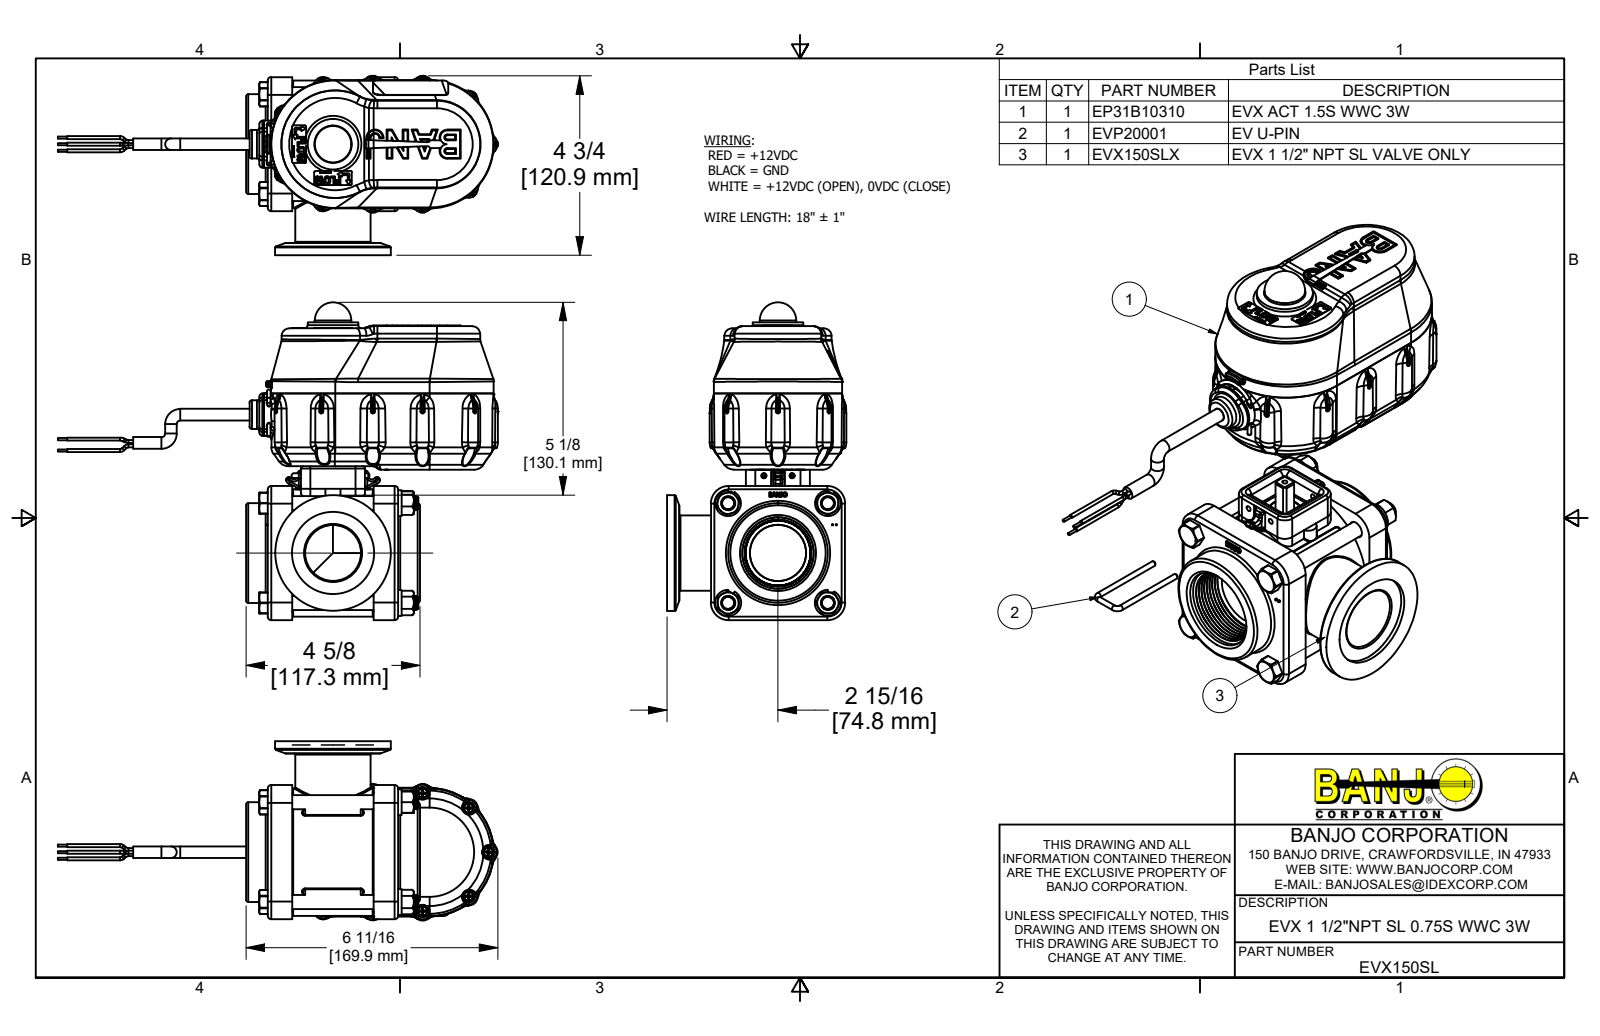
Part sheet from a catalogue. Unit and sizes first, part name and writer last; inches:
Units: inches
Overall size (bounding box): 11.685 × 8.437 × 4.76
Round holes (diameter × count): ⌀0.095 ×11, ⌀0.15 ×11, ⌀0.08 ×7, ⌀0.107 ×4, ⌀0.126 ×4, ⌀0.136 ×4, ⌀0.148 ×4, ⌀0.15 ×4, ⌀0.17 ×4, ⌀0.307 ×4, ⌀0.385 ×4, ⌀0.406 ×4
Round bosses / shafts (diameter × count): ⌀0.324 ×60, ⌀0.25 ×17, ⌀0.08 ×15, ⌀0.14 ×11, ⌀0.108 ×11, ⌀0.085 ×11, ⌀0.058 ×6, ⌀0.375 ×5
Partial cylindrical surfaces — rounded edges, fillets, slot ends (radius × count): R0.013 ×180, R0.04 ×145, R0.01 ×84, R0.02 ×80, R0.005 ×53, R0.03 ×30, R0.06 ×28, R0.08 ×28
Main face-to-face distances: 0.1, 2.565, 0.65, 2.808, 0.211, 0.06, 0.151, 0.125, 1.896, 1.836
Hole centre spacings: 1.872, 2.648, 2.656, 1.662, 1.774, 2.088, 2.69, 2.73
Volume: 65.43 in³ · Surface area: 672.9 in²
Bodies: 98 solids, 11831 faces (3270 planar, 3338 cylindrical, 5223 other)
Part name (STEP PRODUCT): EVX150SL; EP31B10310; B61905PPHS; B632038PM (+8 more)
STEP written by: Autodesk Inventor 2019 (AUTOMOTIVE_DESIGN)
